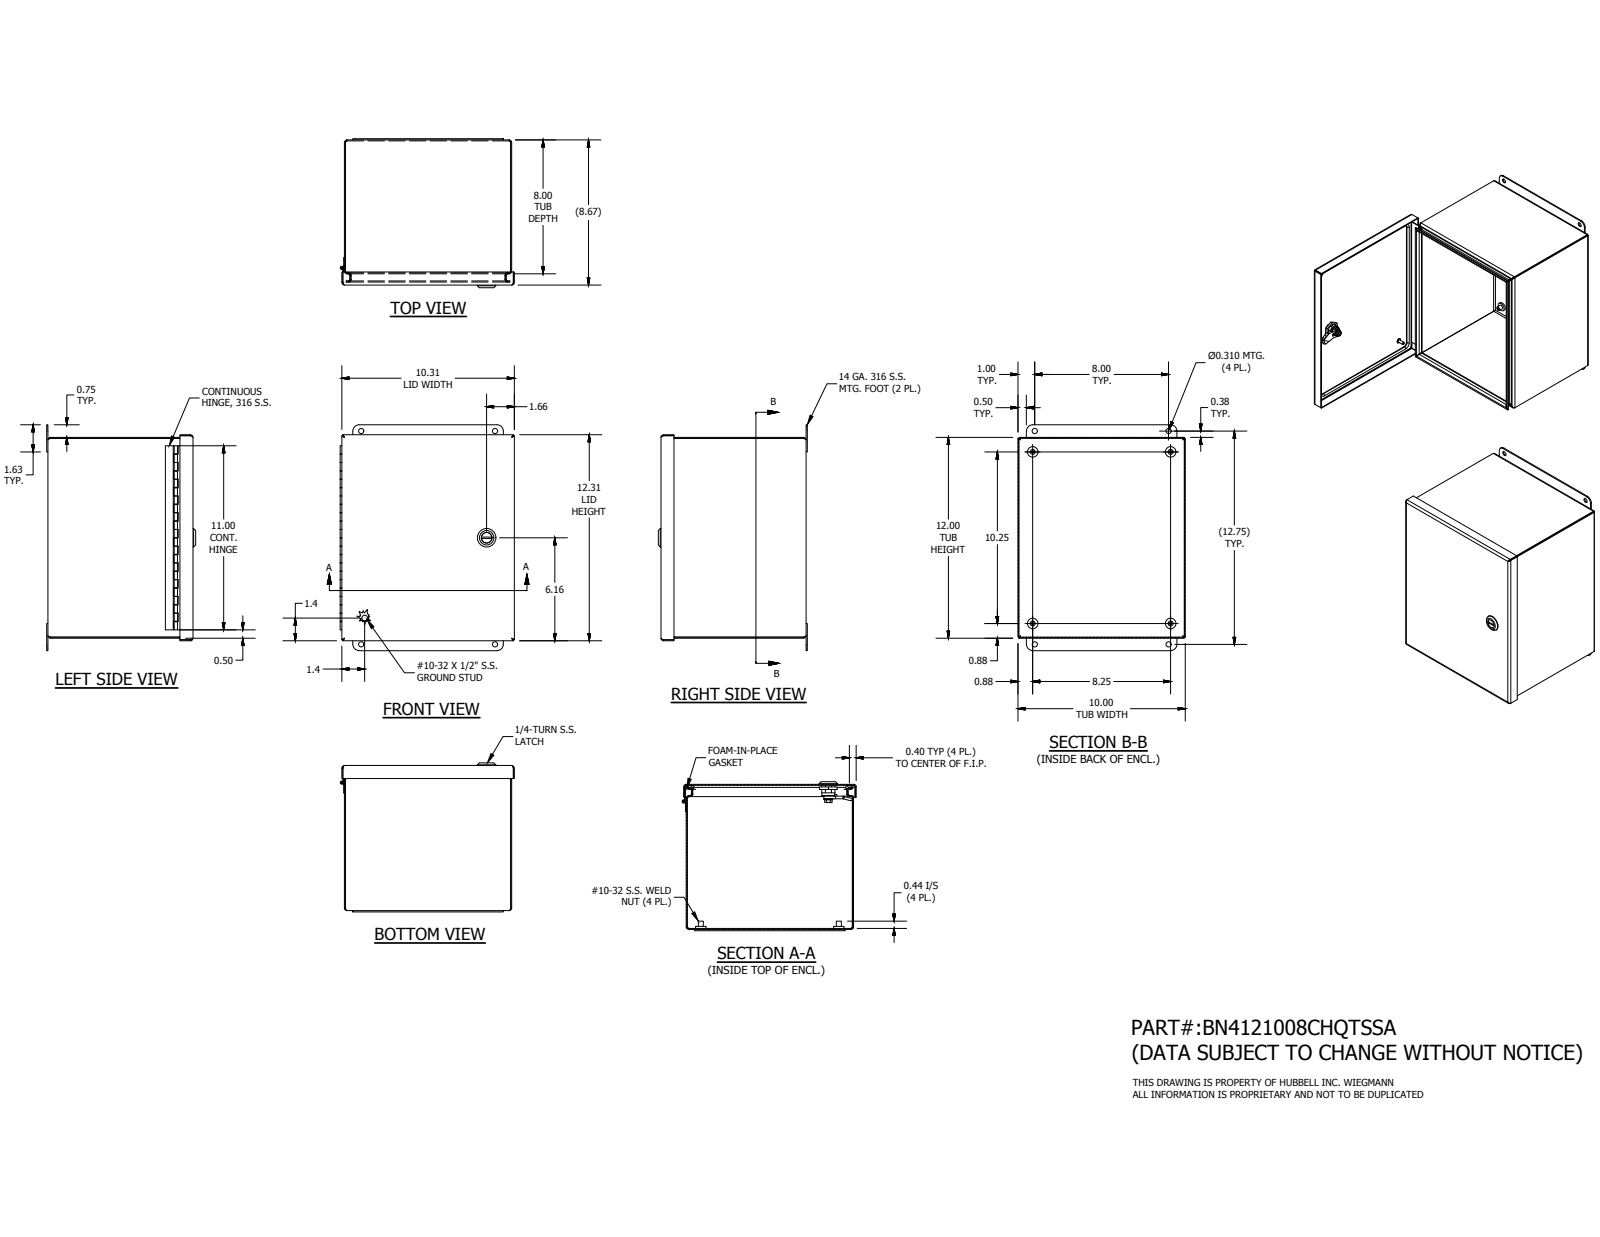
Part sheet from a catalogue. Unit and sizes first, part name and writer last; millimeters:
Units: millimetres
Overall size (bounding box): 342.9 × 264.46 × 226.19
Round holes (diameter × count): ⌀3.96 ×4, ⌀7.87 ×4, ⌀2.96 ×1, ⌀5 ×1, ⌀8 ×1, ⌀10 ×1, ⌀10.2 ×1, ⌀16.1 ×1, ⌀20.38 ×1
Round bosses / shafts (diameter × count): ⌀15.88 ×4, ⌀7.62 ×4, ⌀28 ×1, ⌀19.8 ×1, ⌀16 ×1, ⌀15.2 ×1, ⌀13.5 ×1, ⌀12.8 ×1
Partial cylindrical surfaces — rounded edges, fillets, slot ends (radius × count): R2.38 ×20, R3.88 ×20, R3.17 ×16, R0.5 ×8, R4 ×4, R9.53 ×4, R2.31 ×2, R6.45 ×1
Main face-to-face distances: 1.5, 1.49, 303.3, 218.79, 220.28, 217.29, 218.78, 252.51, 254, 251.01
Hole centre spacings: 31.91, 292.12, 357.65, 131.14, 203.2, 208.8, 208.81, 209.55
Volume: 762 746 mm³ · Surface area: 964 479 mm²
Bodies: 21 solids, 671 faces (366 planar, 208 cylindrical, 97 other)
Part name (STEP PRODUCT): BN41210CHQTSSALID; 12x10; 348130; 32884LH (+8 more)
STEP written by: Autodesk Inventor 2016 (AUTOMOTIVE_DESIGN)
